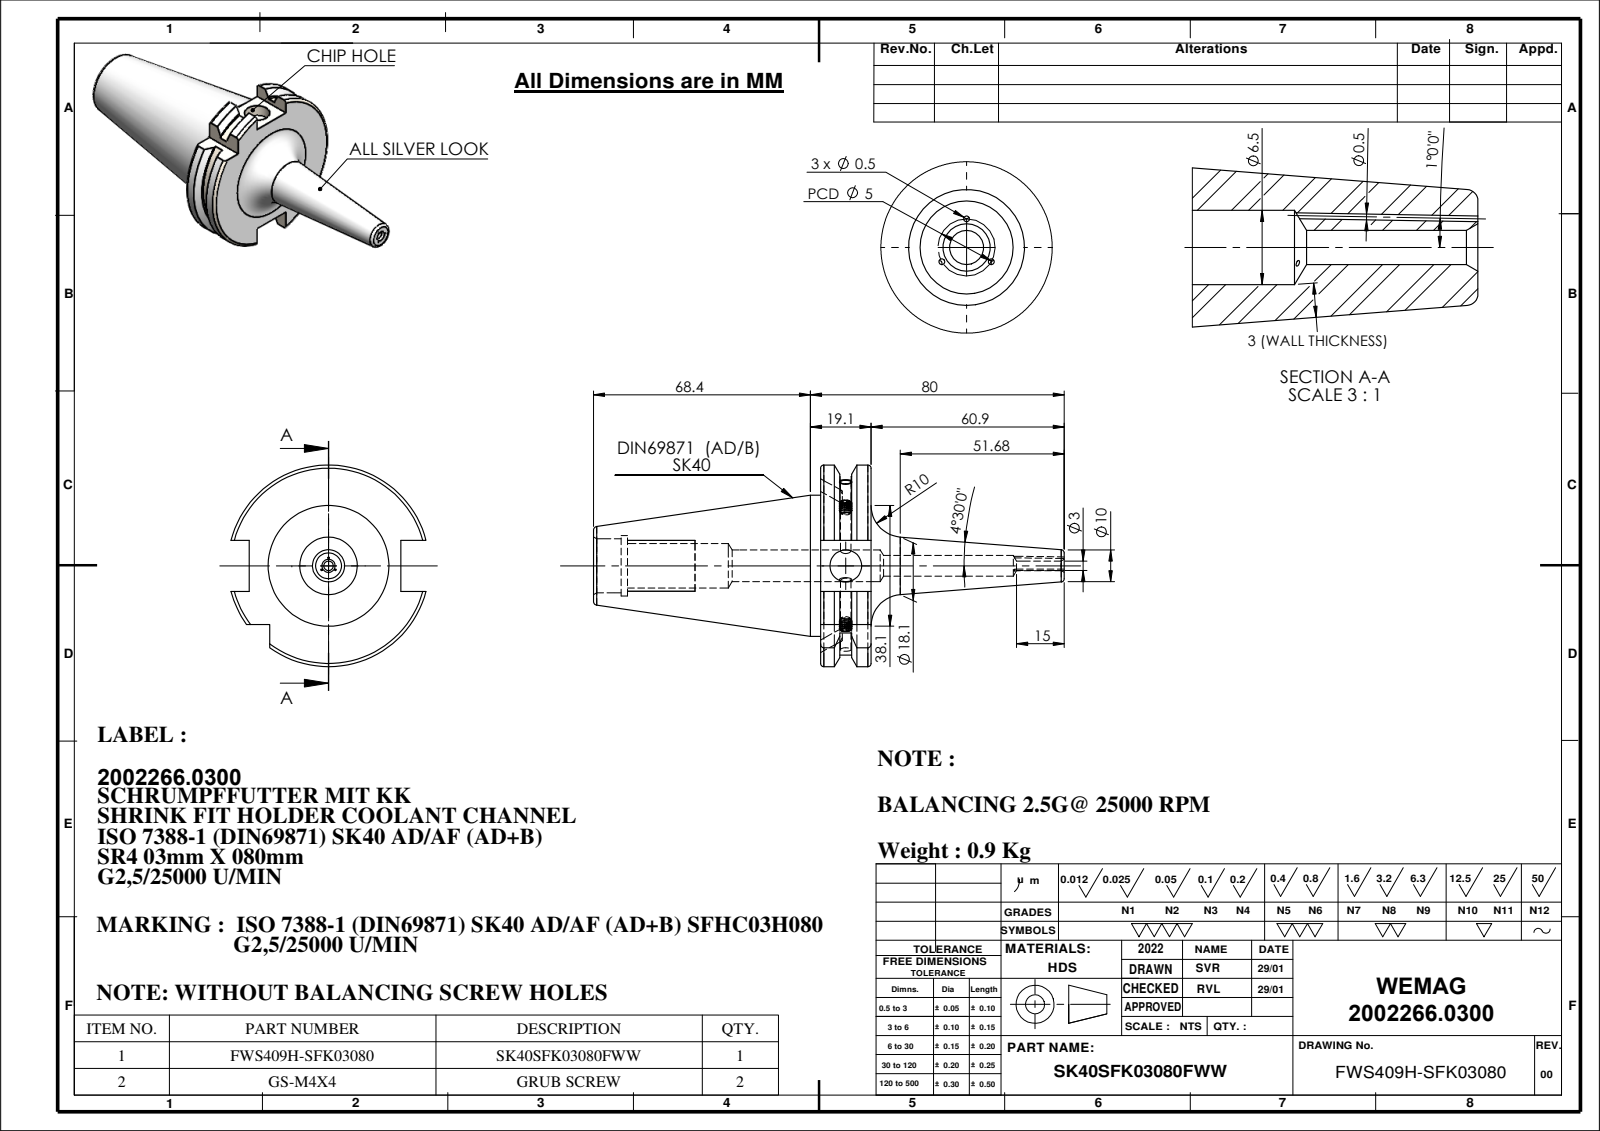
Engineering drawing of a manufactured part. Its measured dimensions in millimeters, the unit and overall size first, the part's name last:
Units: millimetres
Overall size (bounding box): 148.4 × 63.55 × 61.48
Round holes (diameter × count): ⌀0.5 ×3, ⌀10 ×2, ⌀2.99 ×1, ⌀3.3 ×1, ⌀6.5 ×1, ⌀14 ×1, ⌀17 ×1, ⌀19 ×1
Round bosses / shafts (diameter × count): ⌀4 ×2, ⌀44.45 ×1
Partial cylindrical surfaces — rounded edges, fillets, slot ends (radius × count): R28.12 ×1, R31.77 ×1
Main face-to-face distances: 15.9, 16.1, 47.8, 60.9, 76.8, 71.6, 87.5, 10.7, 77.62, 66.92
Volume: 112 043 mm³ · Surface area: 24 776 mm²
Bodies: 3 solids, 200 faces (46 planar, 58 cylindrical, 96 other)
Part name (STEP PRODUCT): 91406-SR403080; GS-M4X4_DIN 913 - M4 x 4-N; SK40SFK03080FWW
STEP written by: SolidWorks 2018 (CONFIG_CONTROL_DESIGN)
